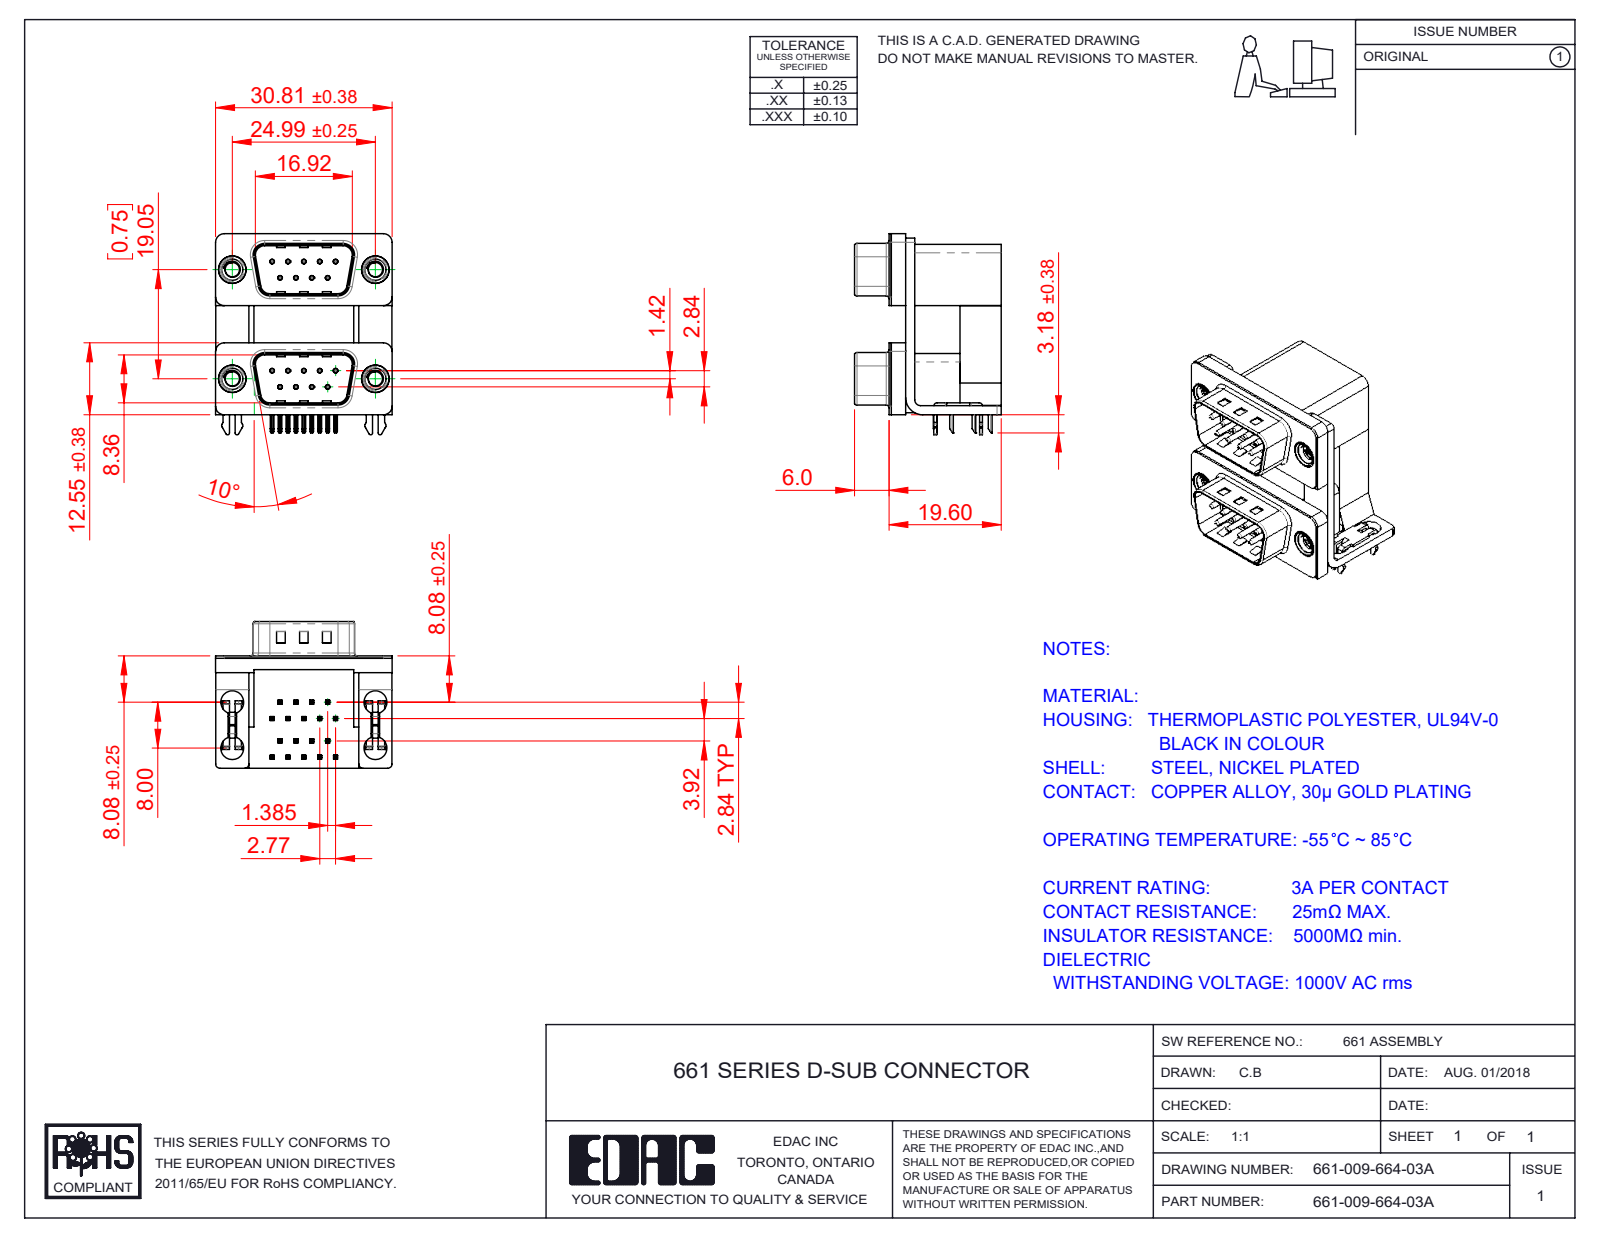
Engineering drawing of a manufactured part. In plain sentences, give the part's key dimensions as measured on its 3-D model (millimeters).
The part is named "661 Threaded Rivet_M3; 661 Housing Upper_09 Contacts M; 661 Shell_09 Contacts; 661-009-664-03A (+8 more)". Its 3-D file was written by "SolidWorks 2020 (CONFIG_CONTROL_DESIGN)". It is 31 solids with 2104 faces: 1254 planar, 652 cylindrical and 198 other. Overall it measures 35.1 by 30.81 by 25.6 millimeters. Its volume is 10 284 cubic millimeters and its surface area 12 079 square millimeters. Round holes: 18 of diameter 0.35, 18 of diameter 0.8, 8 of diameter 4, 4 of diameter 2.5, 4 of diameter 3.5, 4 of diameter 4.8, 4 of diameter 5. Round bosses or shafts: 18 of diameter 0.75, 4 of diameter 4.9, 4 of diameter 4.75, 4 of diameter 3.9. Partial cylindrical surfaces (rounded edges, fillets, slot ends): 82 of radius 0.25, 36 of radius 0.12, 20 of radius 0.5, 14 of radius 1.5, 10 of radius 0.75, 8 of radius 0.9, 8 of radius 1.6, 8 of radius 2. The main face-to-face distances are 0.4, 2.5, 19.05, 16.7, 19.2, 9.5, 7.2, 10.69, 12, 1.6. The hole center spacings are 3.16, 2.77, 19.25, 19.05, 5.54, 19.84, 16.27, 21.93.
